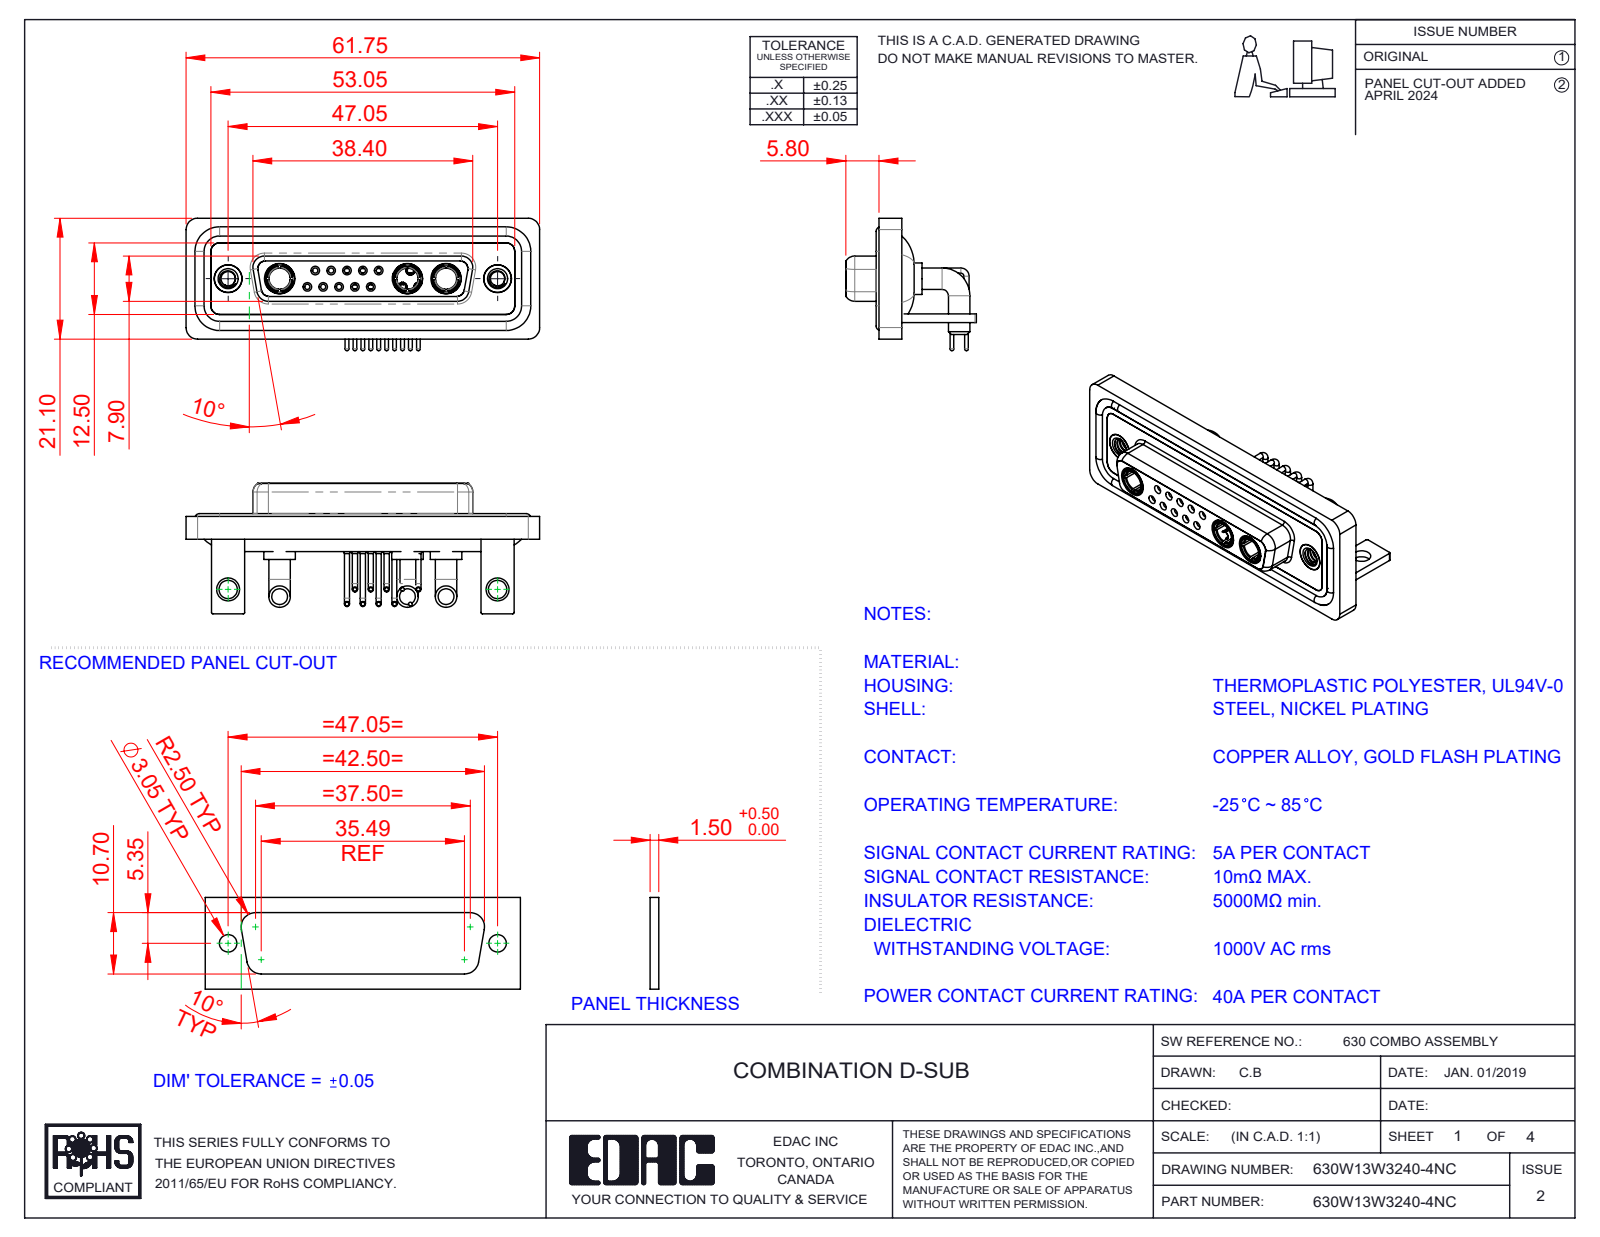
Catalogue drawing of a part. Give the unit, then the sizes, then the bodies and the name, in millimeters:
Units: millimetres
Overall size (bounding box): 61.75 × 23.12 × 22.8
Round holes (diameter × count): ⌀0.9 ×10, ⌀1.1 ×10, ⌀1.5 ×10, ⌀2 ×10, ⌀1.6 ×5, ⌀1.7 ×5, ⌀4.85 ×5, ⌀3.7 ×3, ⌀5.3 ×3, ⌀2.5 ×2, ⌀3.2 ×2, ⌀4 ×2
Round bosses / shafts (diameter × count): ⌀0.9 ×15, ⌀1.6 ×12, ⌀0.65 ×10, ⌀3.75 ×6, ⌀2 ×5, ⌀1.5 ×5, ⌀5.5 ×3, ⌀5.2 ×3
Partial cylindrical surfaces — rounded edges, fillets, slot ends (radius × count): R2 ×19, R1.5 ×18, R0.25 ×16, R1.35 ×8, R1.6 ×8, R0.5 ×5, R0.6 ×4, R0.65 ×4
Main face-to-face distances: 0.4, 1.8, 2.9, 3.7, 1.5, 4.1, 1.1, 1.4, 1.6, 3.1
Hole centre spacings: 3.16, 2.77, 5.54, 5.04, 8.31, 5.03, 7.49, 11.08
Volume: 9 048 mm³ · Surface area: 15 166 mm²
Bodies: 25 solids, 1192 faces (362 planar, 515 cylindrical, 315 other)
Part name (STEP PRODUCT): 630Combo Contact Row 1_50 Contacts; 630W13W3140-4NC; 630Combo Shell Rear_25 Contacts; 630Combo Housing_13W3 (+6 more)
STEP written by: SolidWorks 2023 (CONFIG_CONTROL_DESIGN)
